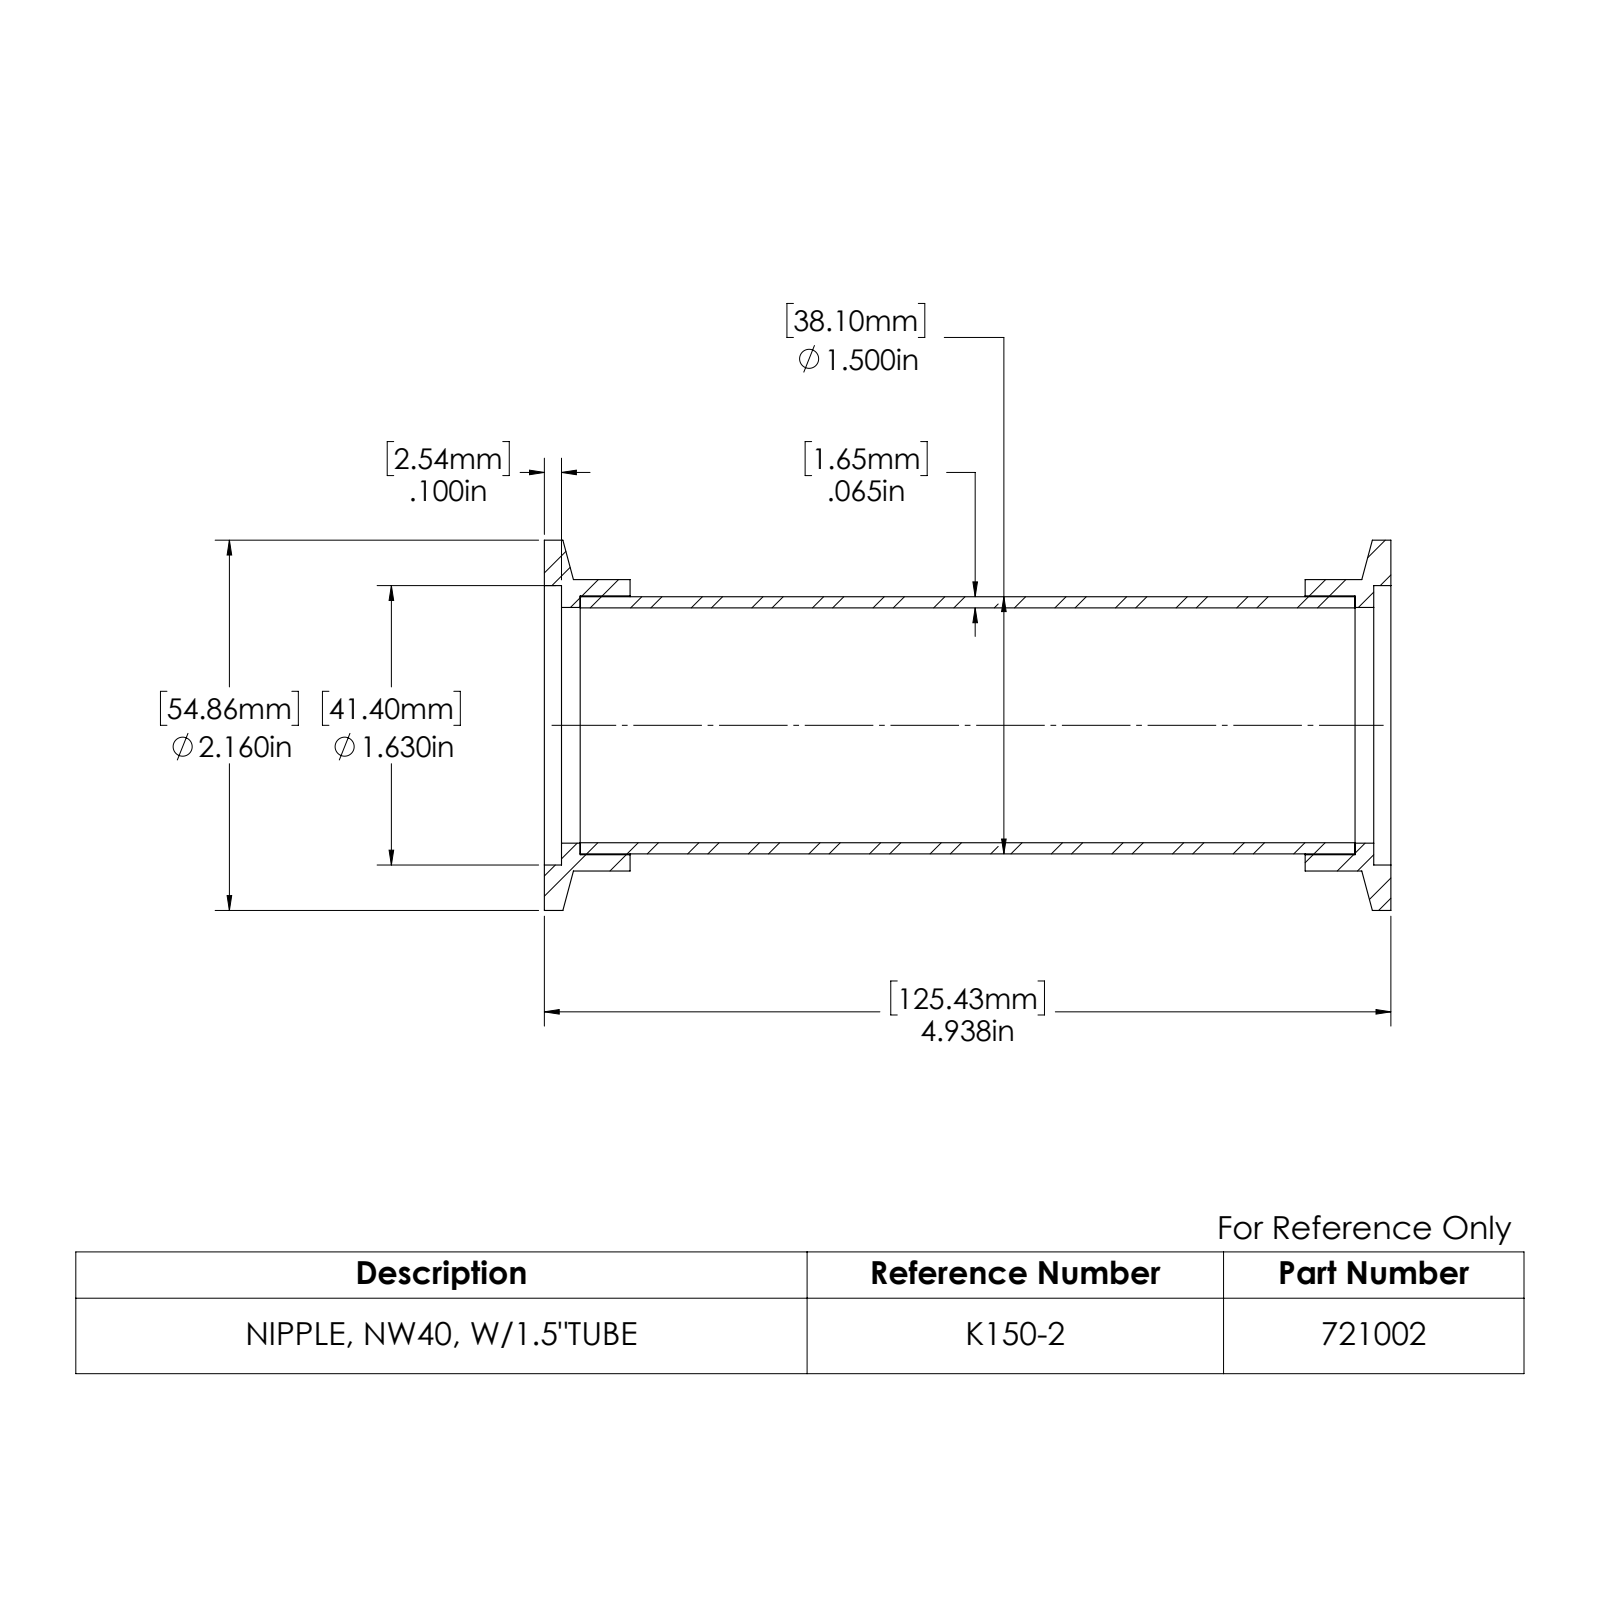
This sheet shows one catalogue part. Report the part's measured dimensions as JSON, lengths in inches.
{"part_name": "713003; 721002; 940202", "step_written_by": "SolidWorks 2022 (AUTOMOTIVE_DESIGN)", "units": "inches", "bodies": {"solids": 3, "faces": 38, "planar": 10, "cylindrical": 24, "other": 4}, "overall_size": [4.938, 2.16, 2.16], "volume_in3": 2.195, "surface_area_in2": 59.88, "round_holes": [[1.37, 1], [1.375, 1], [1.51, 1], [1.63, 1]], "round_bosses_or_shafts": [[2.16, 1], [1.7, 1], [1.5, 1]], "face_to_face_distances": [4.938, 0.1, 4.838, 0.209, 4.729, 0.109, 4.629, 0.5, 4.438, 0.4]}
